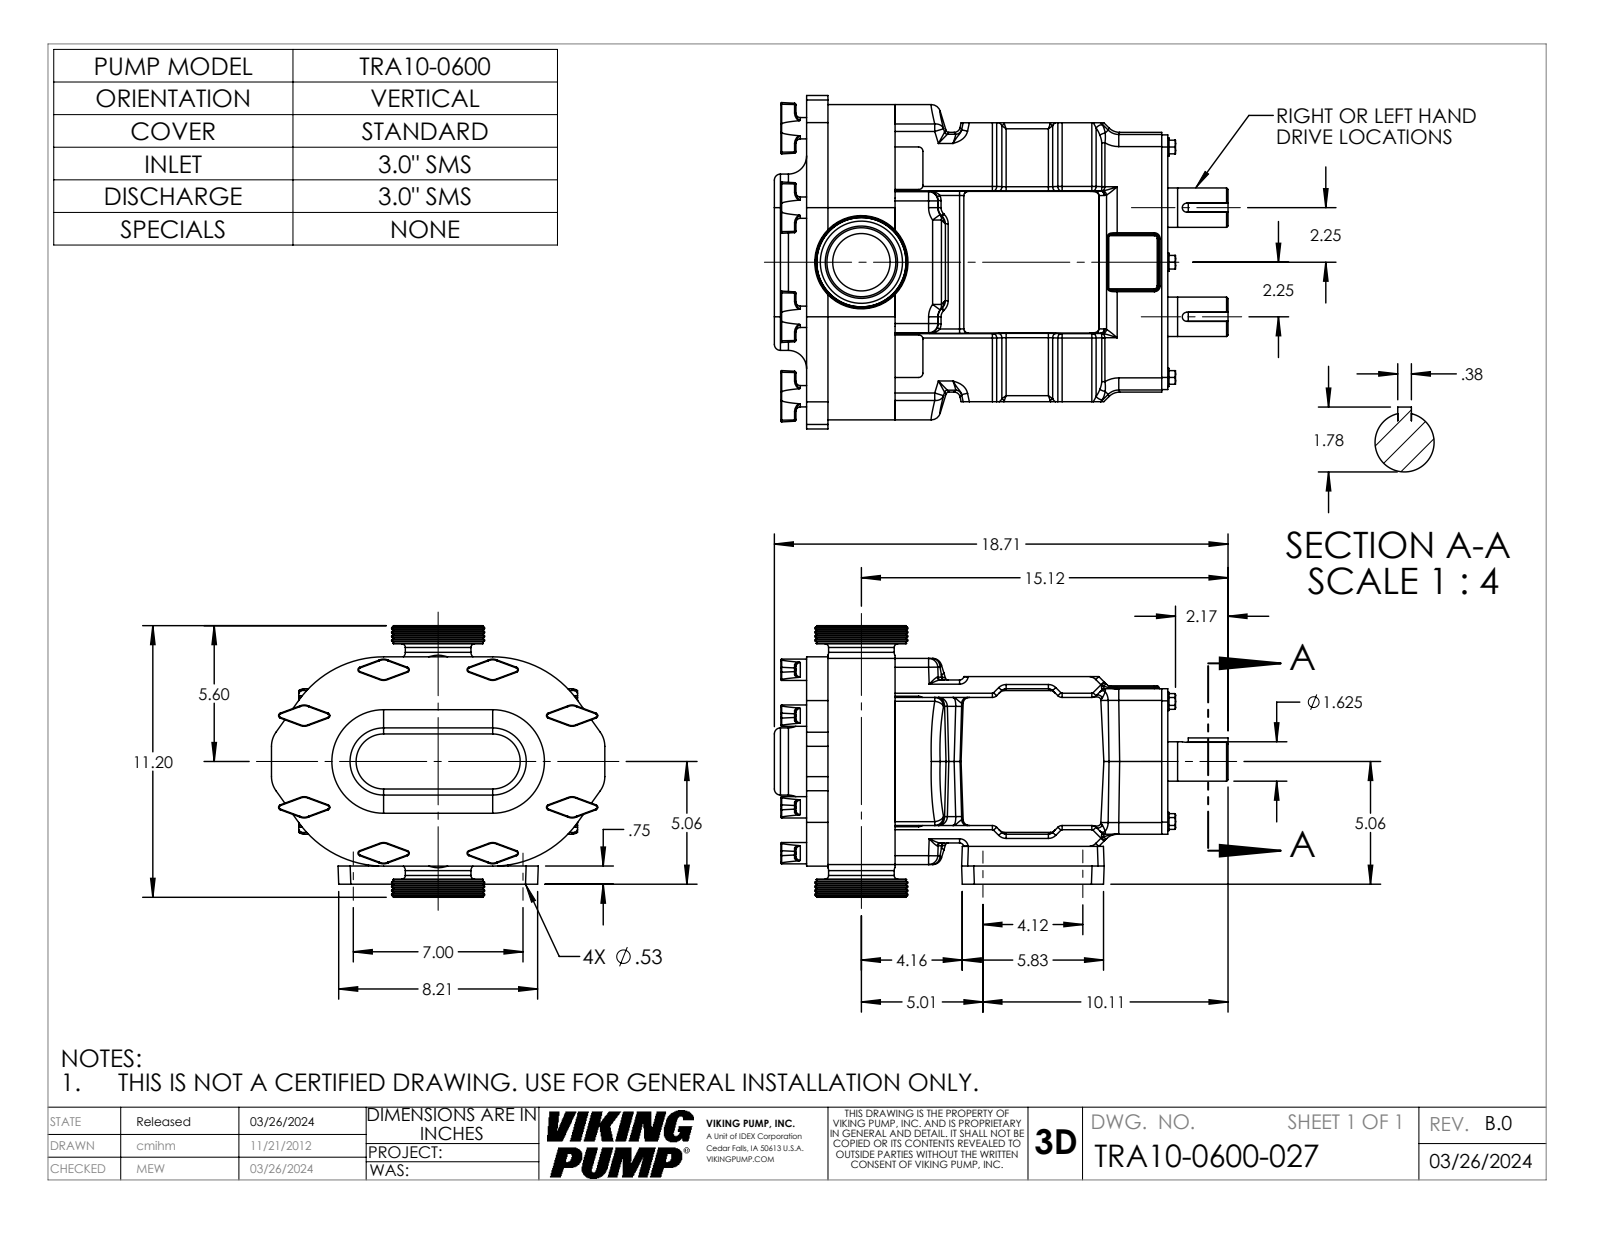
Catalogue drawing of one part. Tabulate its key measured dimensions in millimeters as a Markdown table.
| quantity | value |
| --- | --- |
| part name | TRA10-0600-GEARBOX-V; TRA10-0600-COVER-STD; 0600SMS30; TRA10-0600-027 (+1 more) |
| STEP written by | SolidWorks 2022 (AUTOMOTIVE_DESIGN) |
| units | millimeters |
| bodies | 5 solids, 1137 faces (285 planar, 376 cylindrical, 476 other) |
| overall size | 475.3 × 349.3 × 284.5 |
| volume | 19 520 000 mm³ |
| surface area | 885 800 mm² |
| round holes (diameter × count) | 13.5 × 4, 60.1 × 1, 72.3 × 1, 86.1 × 1 |
| round bosses / shafts (diameter × count) | 22.4 × 8, 19.1 × 6, 41.2 × 2, 75.7 × 1, 68.8 × 1 |
| partial cylindrical surfaces (radius × count) | 4.6 × 44, 1.5 × 43, 0.8 × 32, 6.4 × 32, 9.7 × 28, 3 × 24, 12.7 × 20, 9.5 × 12 |
| main face-to-face distances | 70.3, 22.4, 92.7, 9.1, 378.4, 356.1, 285.8, 143.3, 125.5, 103.1 |
| hole center spacings | 104.6, 155.3, 177.8, 206.3, 248.4 |
